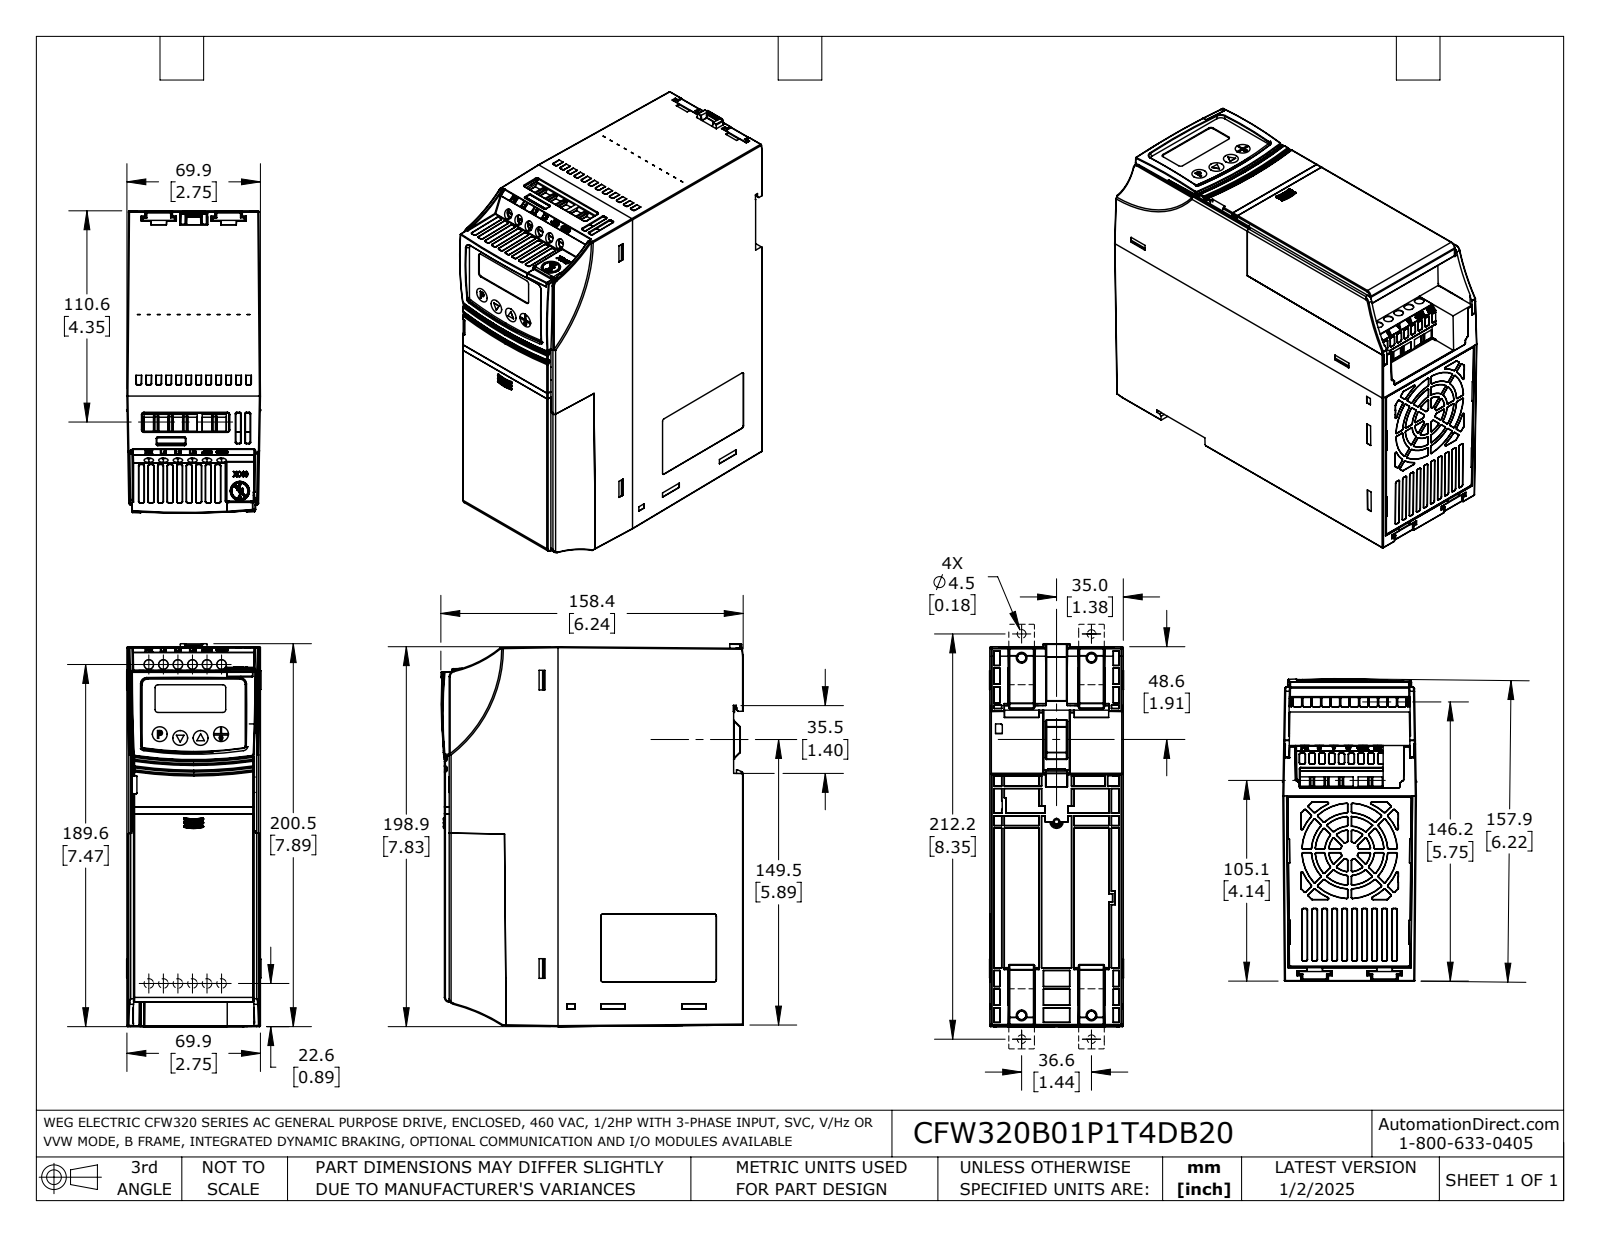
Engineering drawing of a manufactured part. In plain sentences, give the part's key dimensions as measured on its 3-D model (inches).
The part is named "CFW320B01P1T4DB20". Its 3-D file was written by "SolidWorks 2021 (AUTOMOTIVE_DESIGN)". It is 5 solids with 3984 faces: 1907 planar, 899 cylindrical and 1178 other. Overall it measures 7.894 by 6.235 by 2.764 inches. Its volume is 24.51 cubic inches and its surface area 385.1 square inches. Round holes: 6 of diameter 0.193. Partial cylindrical surfaces (rounded edges, fillets, slot ends): 355 of radius 0.012, 181 of radius 0.02, 14 of radius 0.039, 7 of radius 0.03, 5 of radius 0.118, 2 of radius 0.01, 2 of radius 0.109, 1 of radius 0.098. The main face-to-face distances are 0.209, 0.098, 0.1, 5.826, 5.728, 0.211, 5.939, 6.037, 7.5, 0.039. The hole center spacings are 0.3, 0.6, 0.9, 1.2, 1.5.
